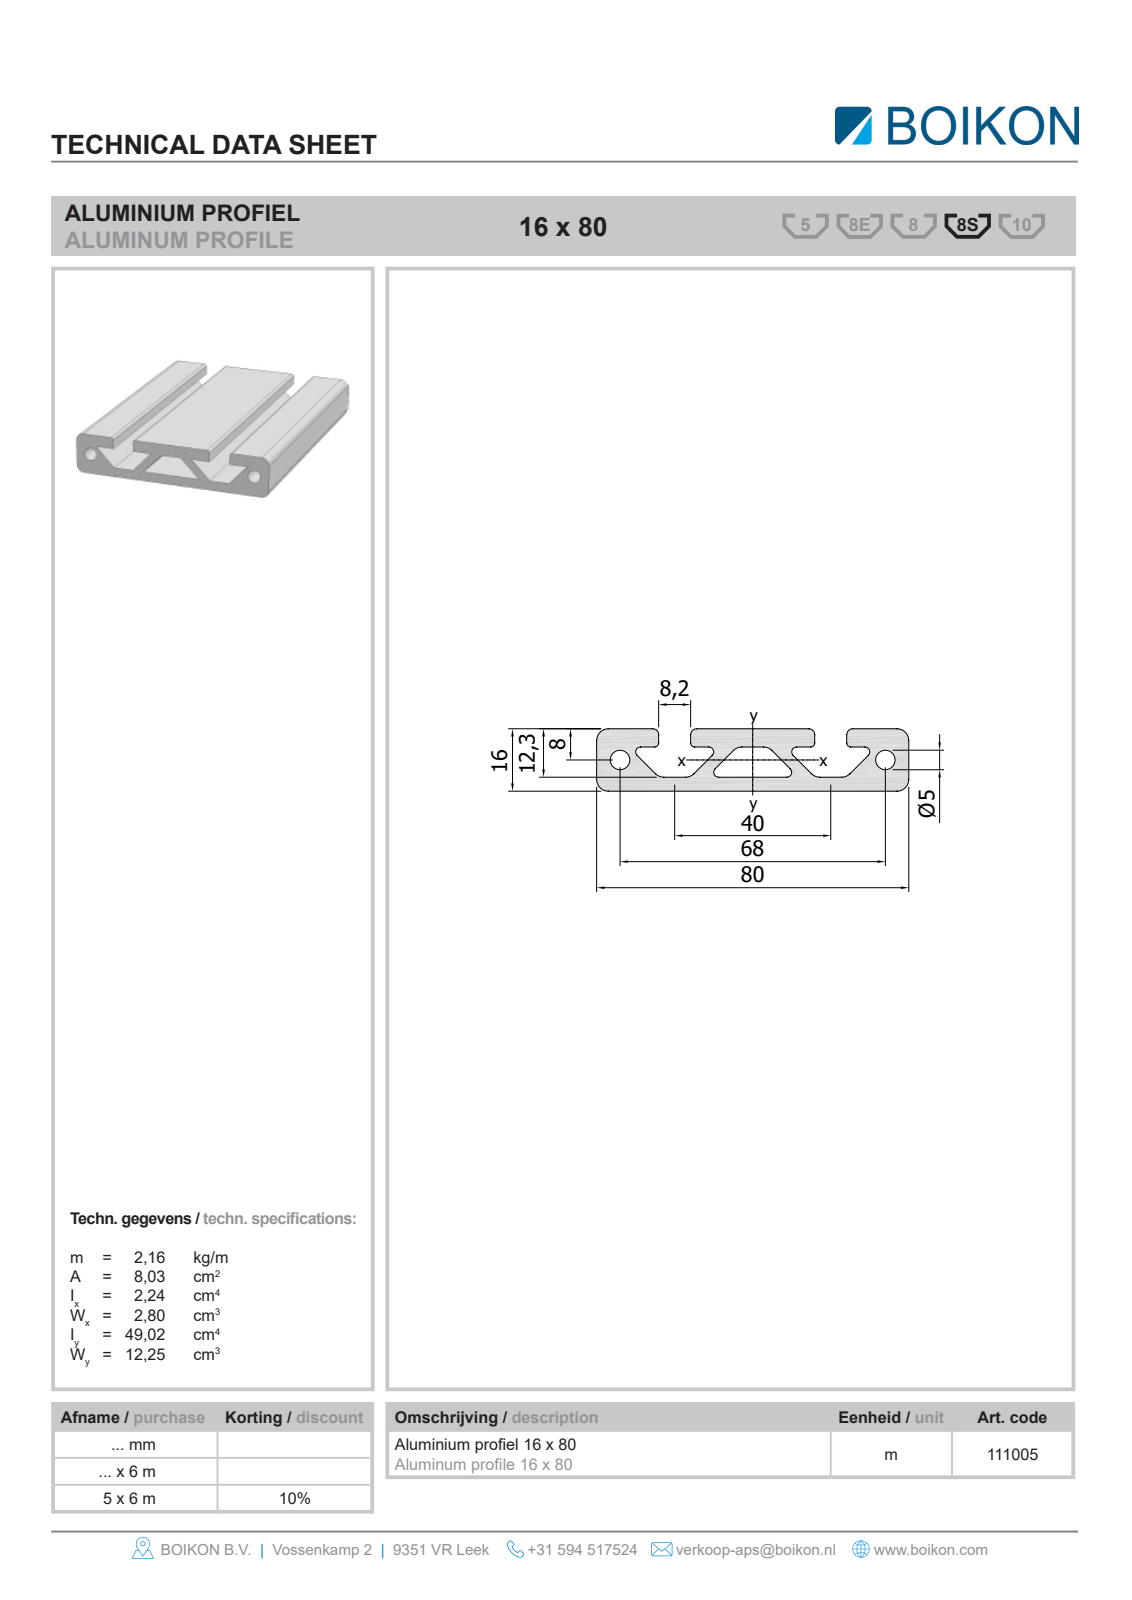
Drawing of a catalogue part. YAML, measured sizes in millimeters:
part_name: "Root; 11100516x80BOIKON0"
step_written_by: "HiCAD 2013 1802.4 Build 509 (AUTOMOTIVE_DESIGN)"
units: millimeters
bodies: {solids: 1, faces: 36, planar: 26, cylindrical: 10, other: 0}
overall_size: [1000, 80, 16]
volume: 797971
surface_area: 361054
round_holes:
  - {diameter: 5, count: 2}
partial_cylinders:
  - {radius: 1, count: 4}
  - {radius: 3, count: 4}
face_to_face_distances: [16, 3.75, 12.25, 11.5, 7.75, 4.5, 28.76, 25.53, 3.23, 3.24]
hole_center_spacings: [68]
